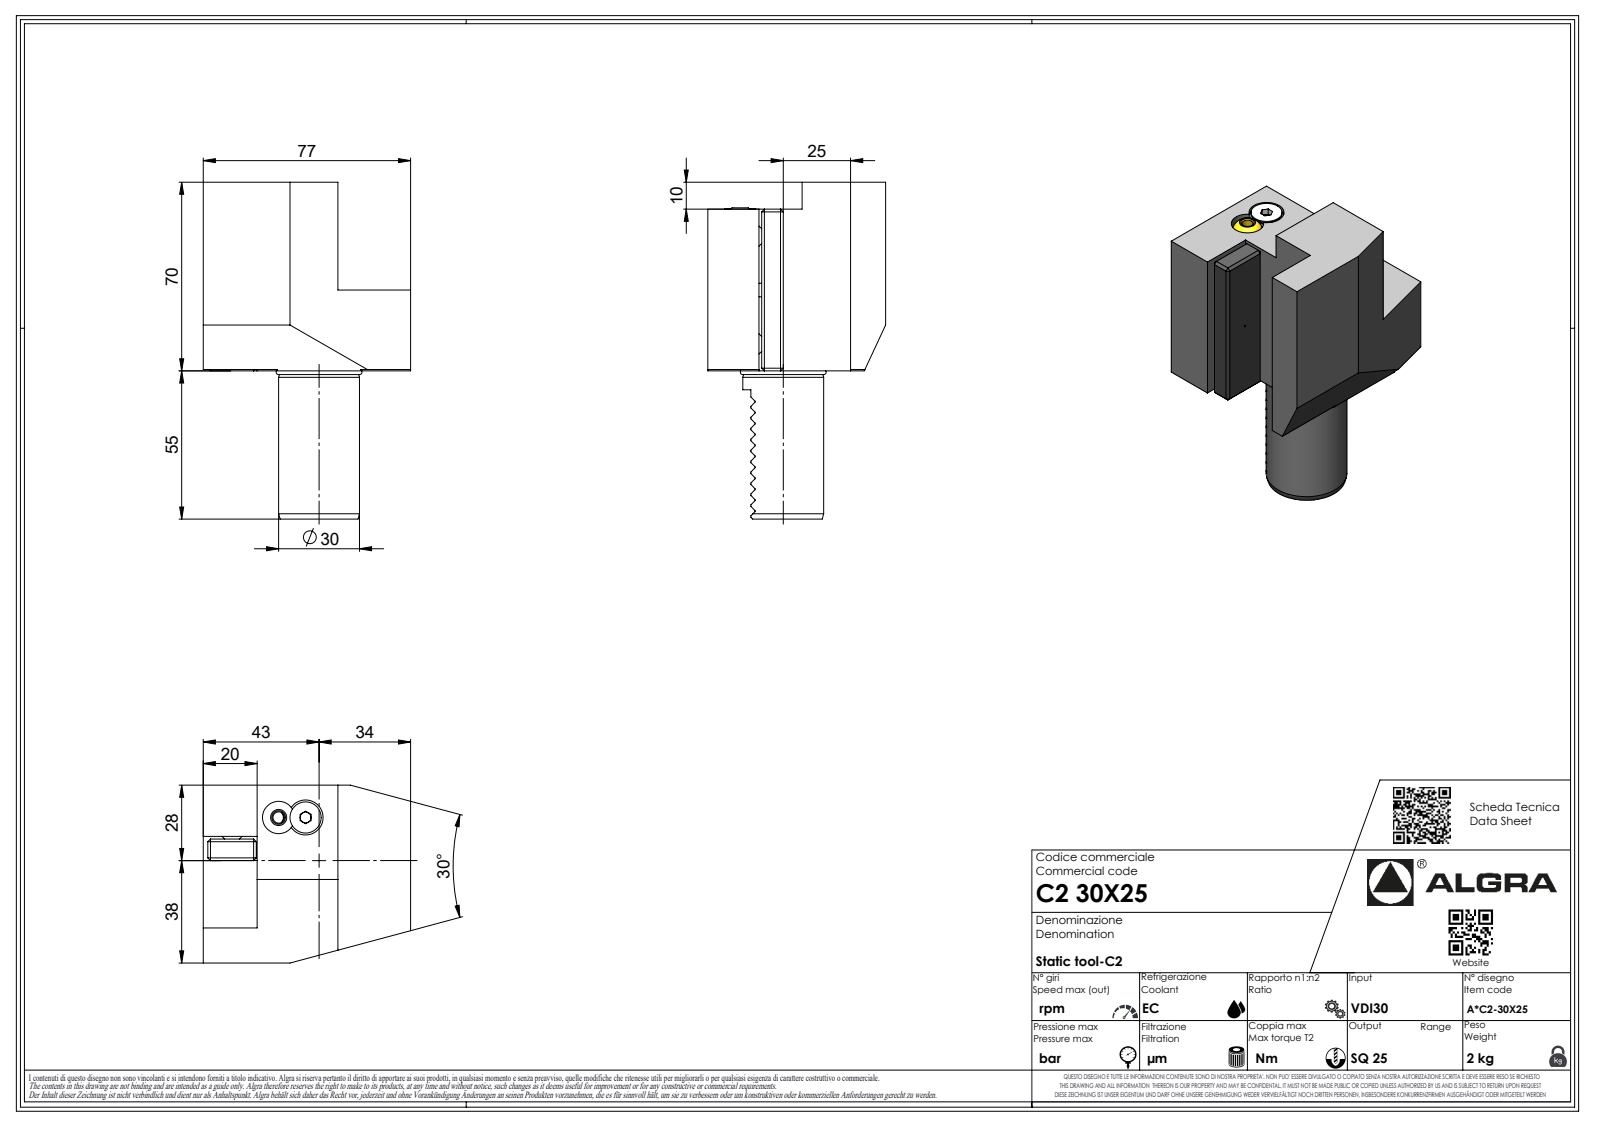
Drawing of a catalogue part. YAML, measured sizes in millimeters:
part_name: "C230X25"
step_written_by: "SolidWorks 2023 (AUTOMOTIVE_DESIGN)"
units: millimeters
bodies: {solids: 1, faces: 324, planar: 219, cylindrical: 42, other: 63}
overall_size: [125, 77, 66]
volume: 253360
surface_area: 33650
round_holes:
  - {diameter: 2.1, count: 1}
round_bosses_or_shafts:
  - {diameter: 30, count: 1}
  - {diameter: 29.1, count: 1}
  - {diameter: 6.37, count: 1}
  - {diameter: 1.7, count: 1}
partial_cylinders:
  - {radius: 0.3, count: 11}
  - {radius: 0.33, count: 7}
  - {radius: 0.52, count: 7}
  - {radius: 3.7, count: 7}
  - {radius: 0.21, count: 1}
  - {radius: 34, count: 1}
face_to_face_distances: [30, 50, 20, 66, 60, 77, 57, 27, 13, 53]
